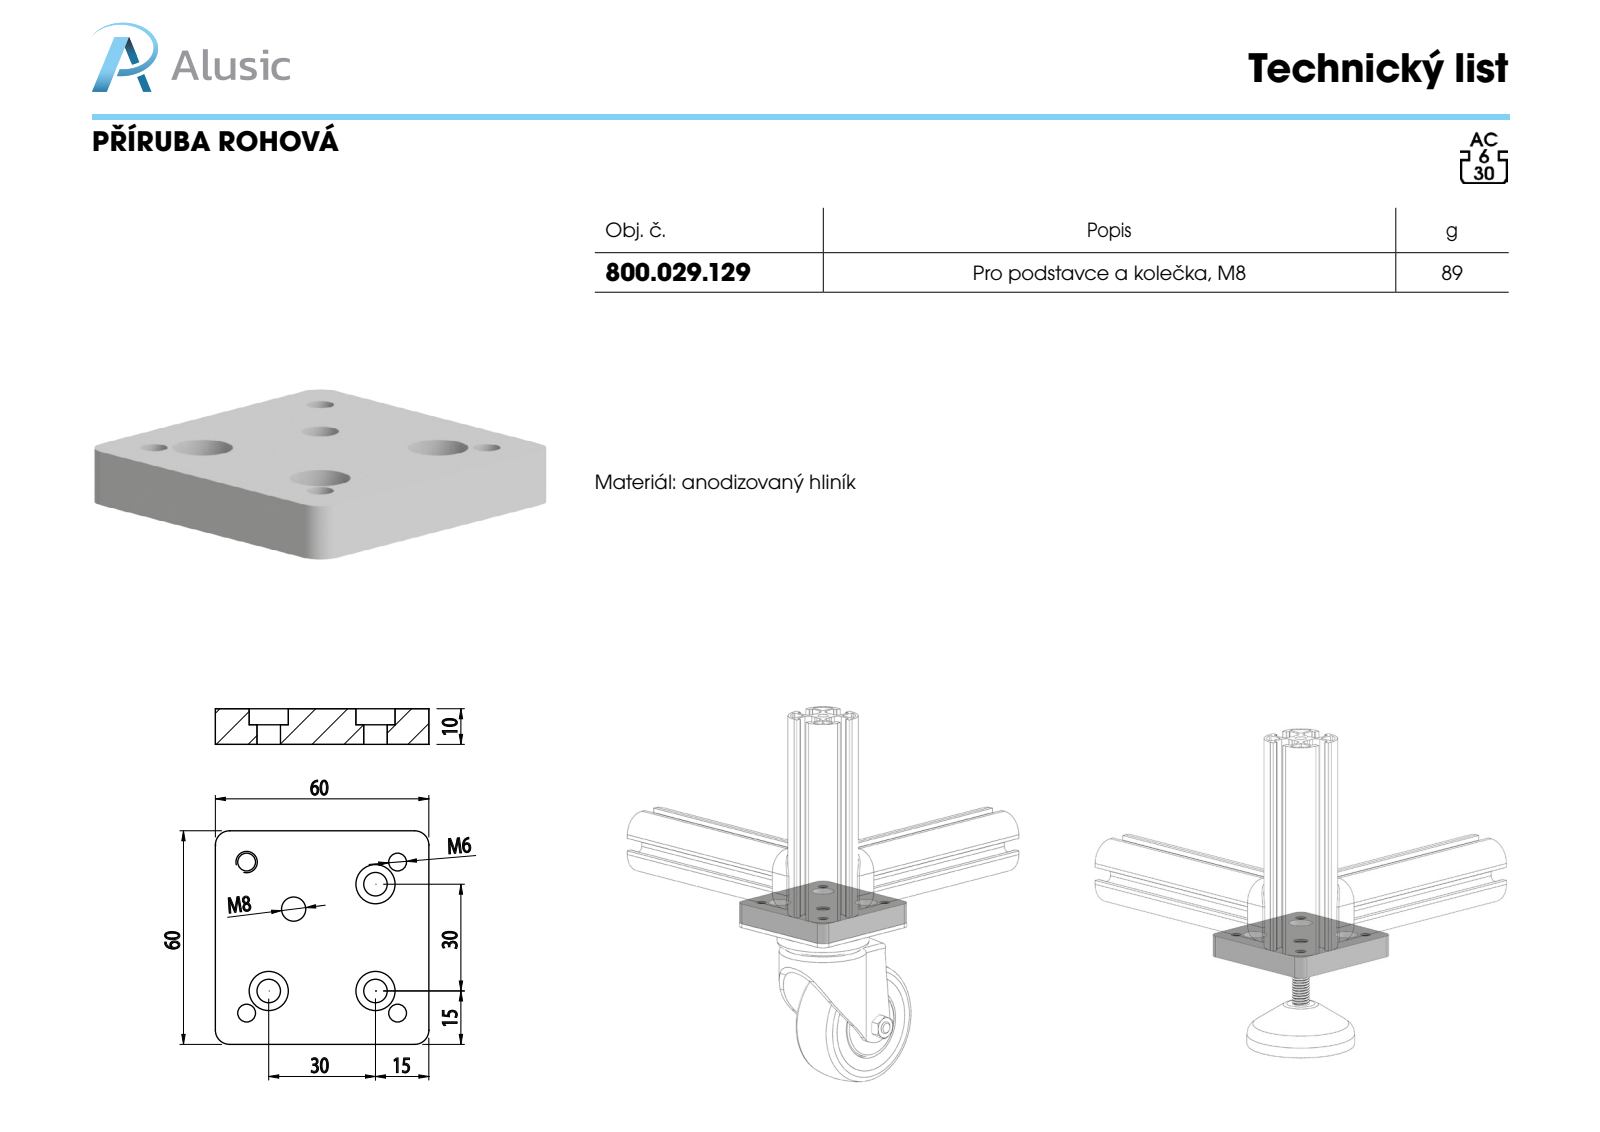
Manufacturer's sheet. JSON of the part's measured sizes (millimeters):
{"part_name": "800.029.129", "step_written_by": "SolidWorks 2012 (CONFIG_CONTROL_DESIGN)", "units": "millimeters", "bodies": {"solids": 1, "faces": 35, "planar": 9, "cylindrical": 26, "other": 0}, "overall_size": [60, 60, 10], "volume_mm3": 32867, "surface_area_mm2": 10719, "round_holes": [[5, 4], [6.6, 3], [11, 3], [6.8, 1]], "partial_cylinders_radius": [[4, 4]], "face_to_face_distances": [10, 60, 5.5, 4.5], "hole_center_spacings": [36.74, 42.42, 8.78, 51.21, 24.04, 30, 32.06, 59.99]}
